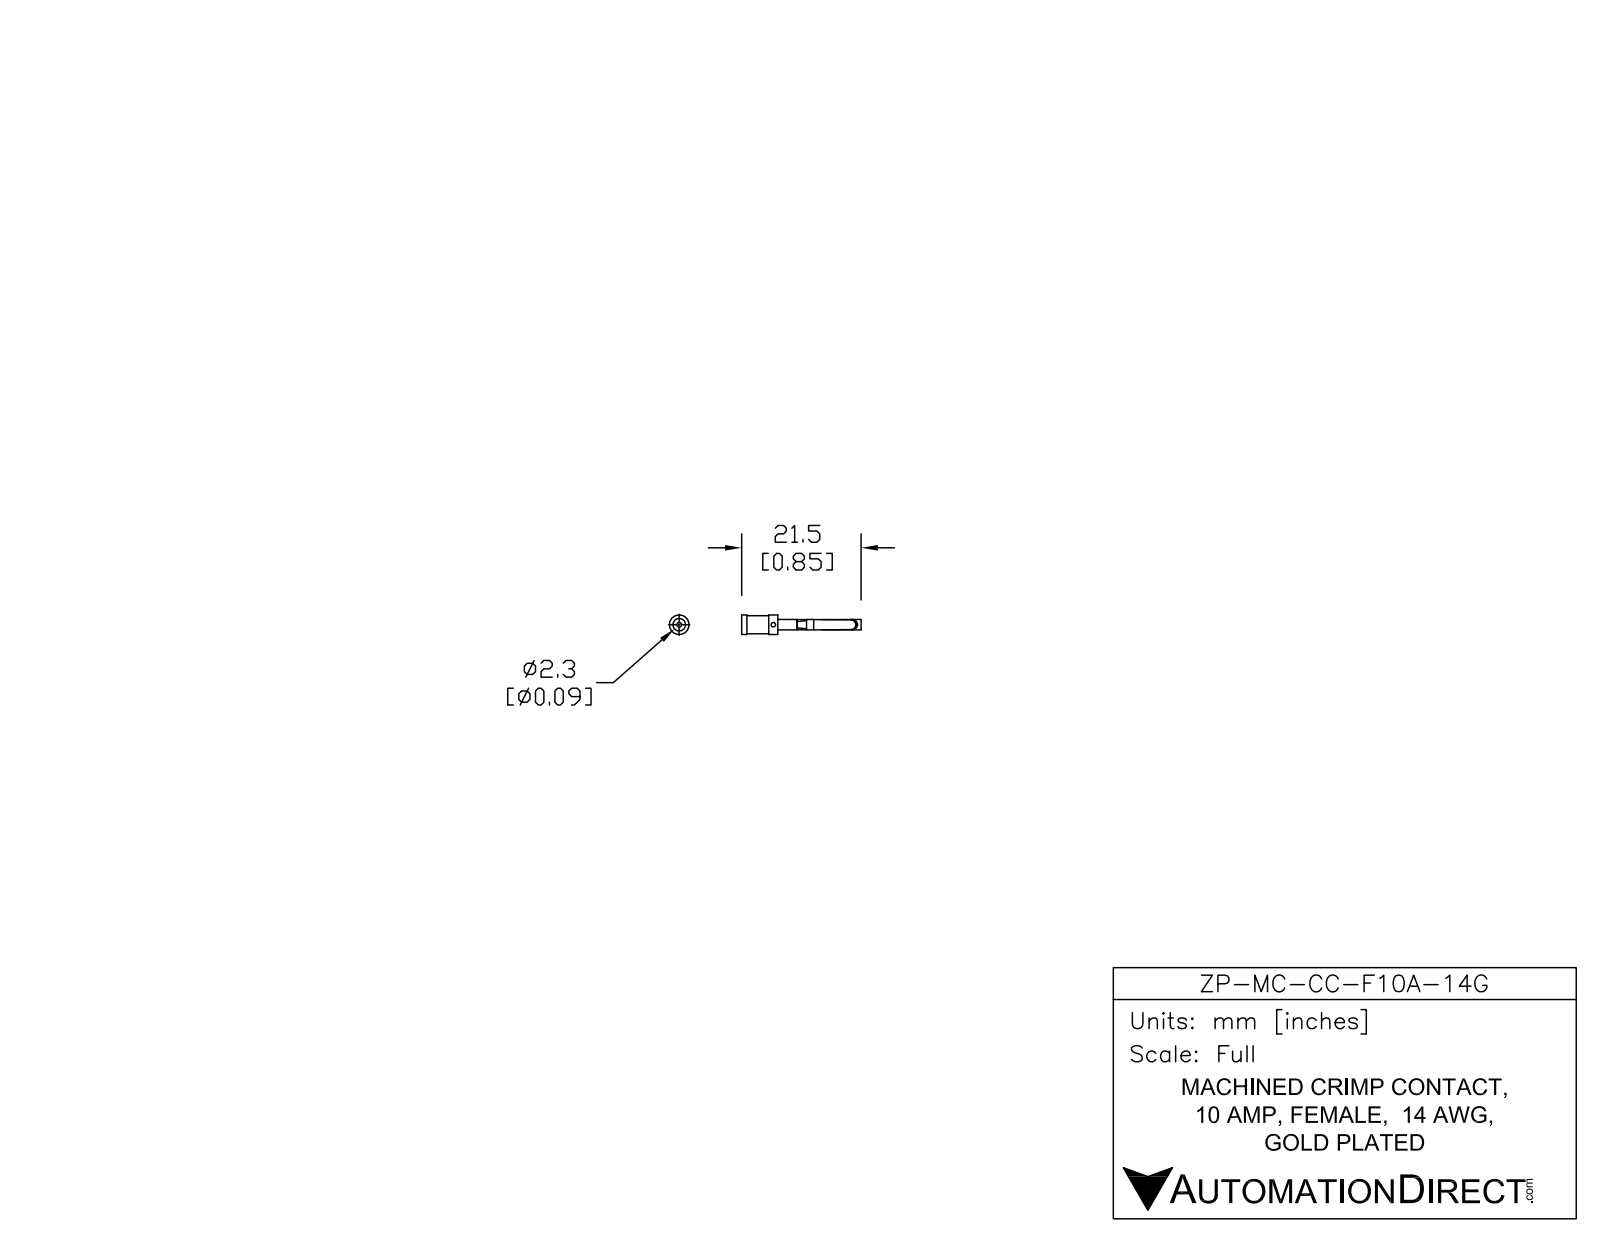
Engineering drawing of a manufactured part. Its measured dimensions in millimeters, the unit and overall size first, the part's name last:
Units: millimetres
Overall size (bounding box): 21.5 × 3.52 × 3.52
Round holes (diameter × count): ⌀0.8 ×1, ⌀0.85 ×1, ⌀1.46 ×1
Round bosses / shafts (diameter × count): ⌀3.52 ×1, ⌀3.25 ×1, ⌀1.88 ×1, ⌀1.66 ×1
Main face-to-face distances: 6.51, 10, 3.49, 11.5, 1.84, 1.5, 4.99, 6.62, 5.12, 1.63
Volume: 76 mm³ · Surface area: 260 mm²
Bodies: 1 solid, 52 faces (25 planar, 18 cylindrical, 9 other)
Part name (STEP PRODUCT): ZP-MC-CC-F10A-14G
STEP written by: SolidWorks 2014 (AUTOMOTIVE_DESIGN)
